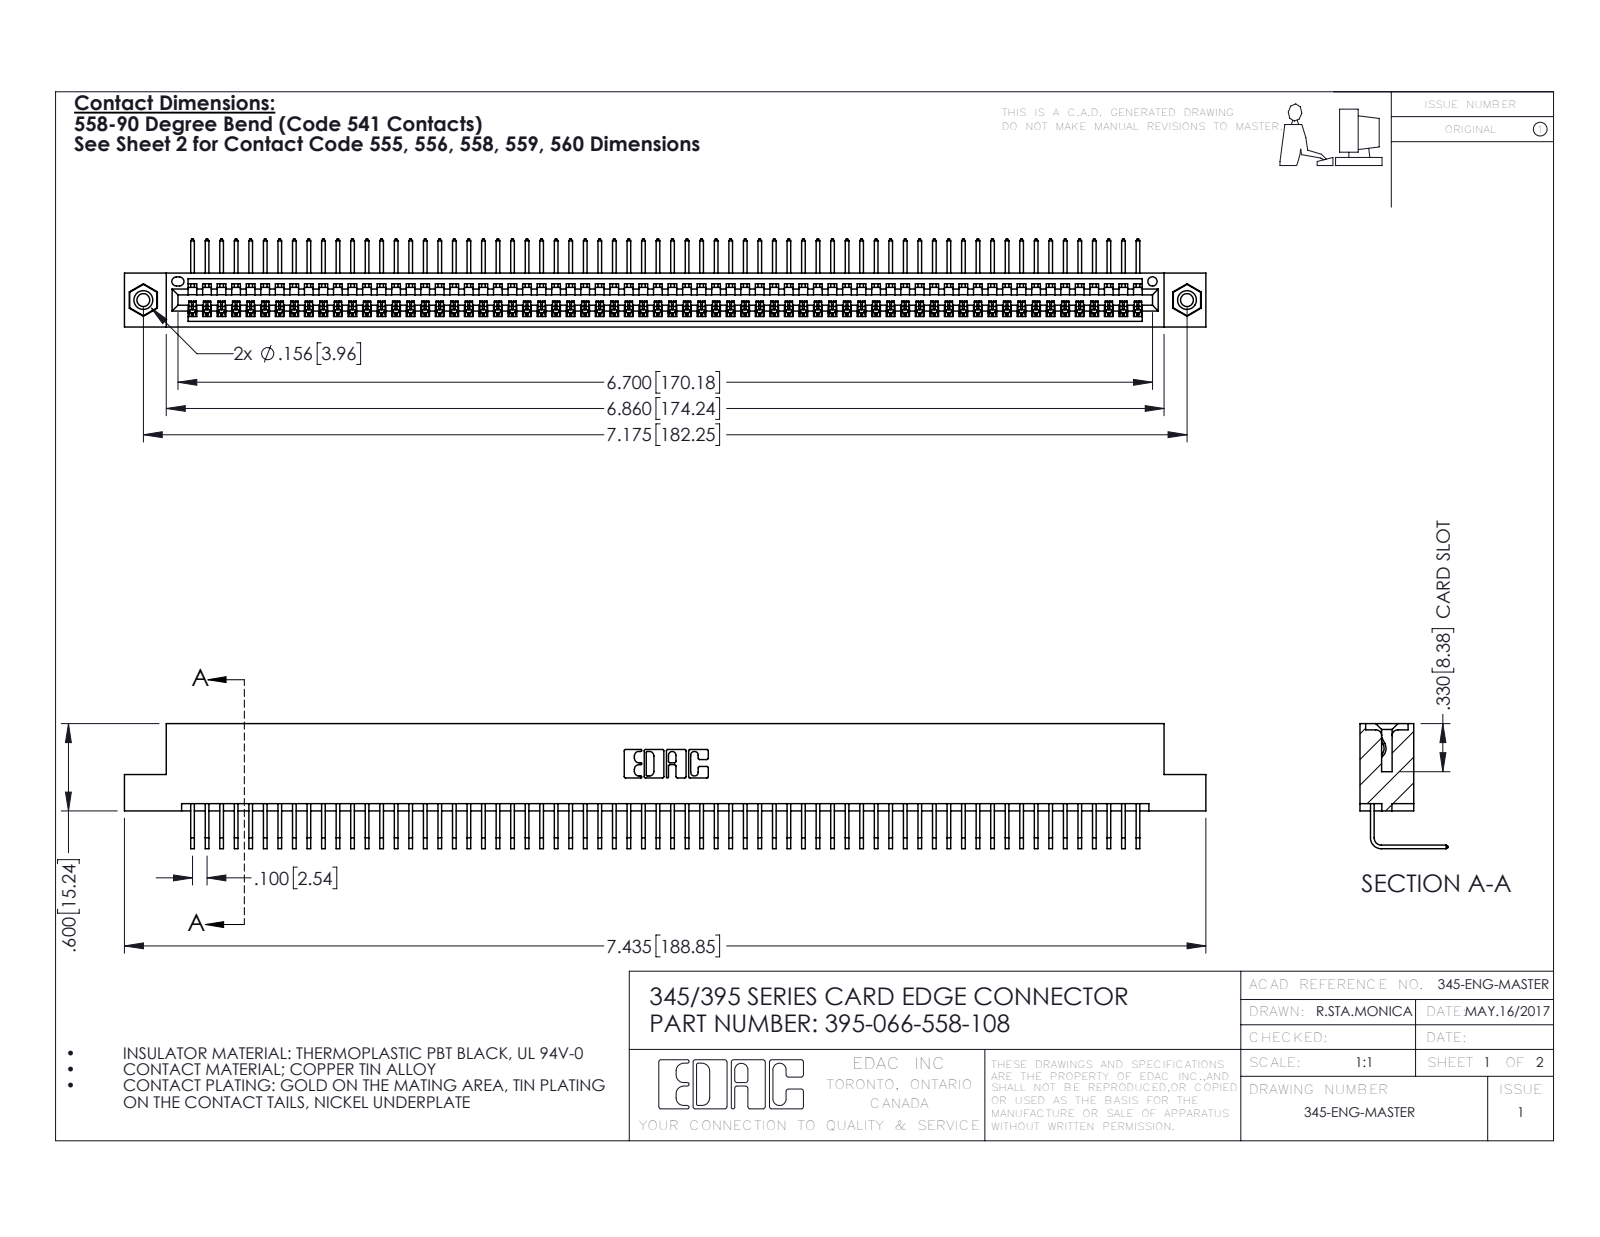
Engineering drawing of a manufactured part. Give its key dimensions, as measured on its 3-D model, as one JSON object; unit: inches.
{"part_name": "395-066-558-108; 345 Part_Flush Mounting Lugs - 0.156 Dia-TI; 345-292-001_558 Tail - 2; 345-250-001_345-250-003-102", "step_written_by": "SolidWorks 2016 (CONFIG_CONTROL_DESIGN)", "units": "inches", "bodies": {"solids": 69, "faces": 4146, "planar": 2884, "cylindrical": 1246, "other": 16}, "overall_size": [7.435, 0.859, 0.605], "volume_in3": 1.12, "surface_area_in2": 40.33, "round_holes": [[0.089, 2], [0.125, 2], [0.156, 2], [0.064, 1]], "round_bosses_or_shafts": [[0.155, 2]], "partial_cylinders_radius": [[0.006, 132], [0.01, 22], [0.007, 6], [0.031, 6], [0.026, 3], [0.031, 2], [0.04, 2], [0.014, 1]], "face_to_face_distances": [0.072, 0.298, 0.37, 0.2, 0.098, 0.272, 0.025, 0.225, 0.149, 0.072], "hole_center_spacings": [0.27, 6.939, 7.175]}
